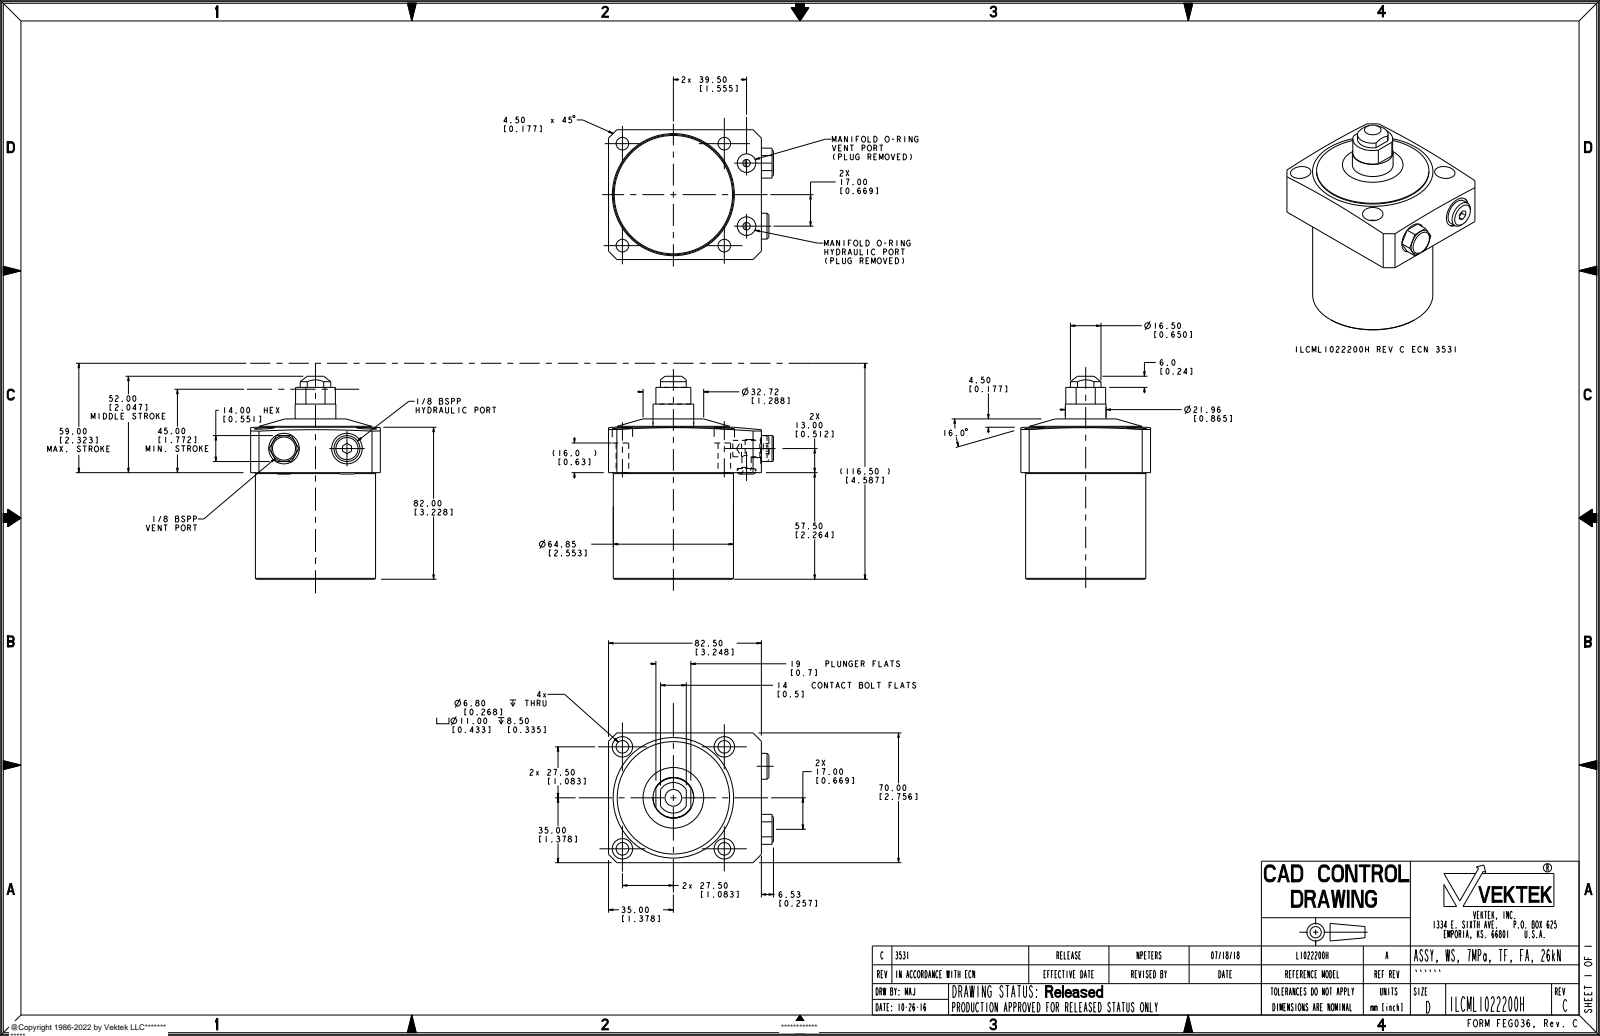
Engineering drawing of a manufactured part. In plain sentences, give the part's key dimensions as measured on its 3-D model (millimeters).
The part is named "ILCML1022200H". Its 3-D file was written by "PRO/ENGINEER BY PARAMETRIC TECHNOLOGY CORPORATION, 2013320 (AUTOMOTIVE_DESIGN)". It is 4 solids with 142 faces: 56 planar, 54 cylindrical and 32 other. Overall it measures 109.5 by 89.03 by 70 millimeters. Its volume is 338 363 cubic millimeters and its surface area 37 517 square millimeters. Round holes: 4 of diameter 6.8, 4 of diameter 11, 2 of diameter 5, 2 of diameter 6, 2 of diameter 8.84, 2 of diameter 10, 2 of diameter 16.5, 1 of diameter 21.98. Round bosses or shafts: 1 of diameter 64.85, 1 of diameter 60.62, 1 of diameter 21.96, 1 of diameter 13.97, 1 of diameter 9.73, 1 of diameter 9.72. Partial cylindrical surfaces (rounded edges, fillets, slot ends): 1 of radius 8.25, 1 of radius 10.75. The main face-to-face distances are 57.5, 70, 82.5, 86.5, 29, 82, 24.5, 4.5, 82.25, 101.46. The hole center spacings are 38.89, 55, 15.95, 34, 43, 46.09, 67.82, 77.78.
